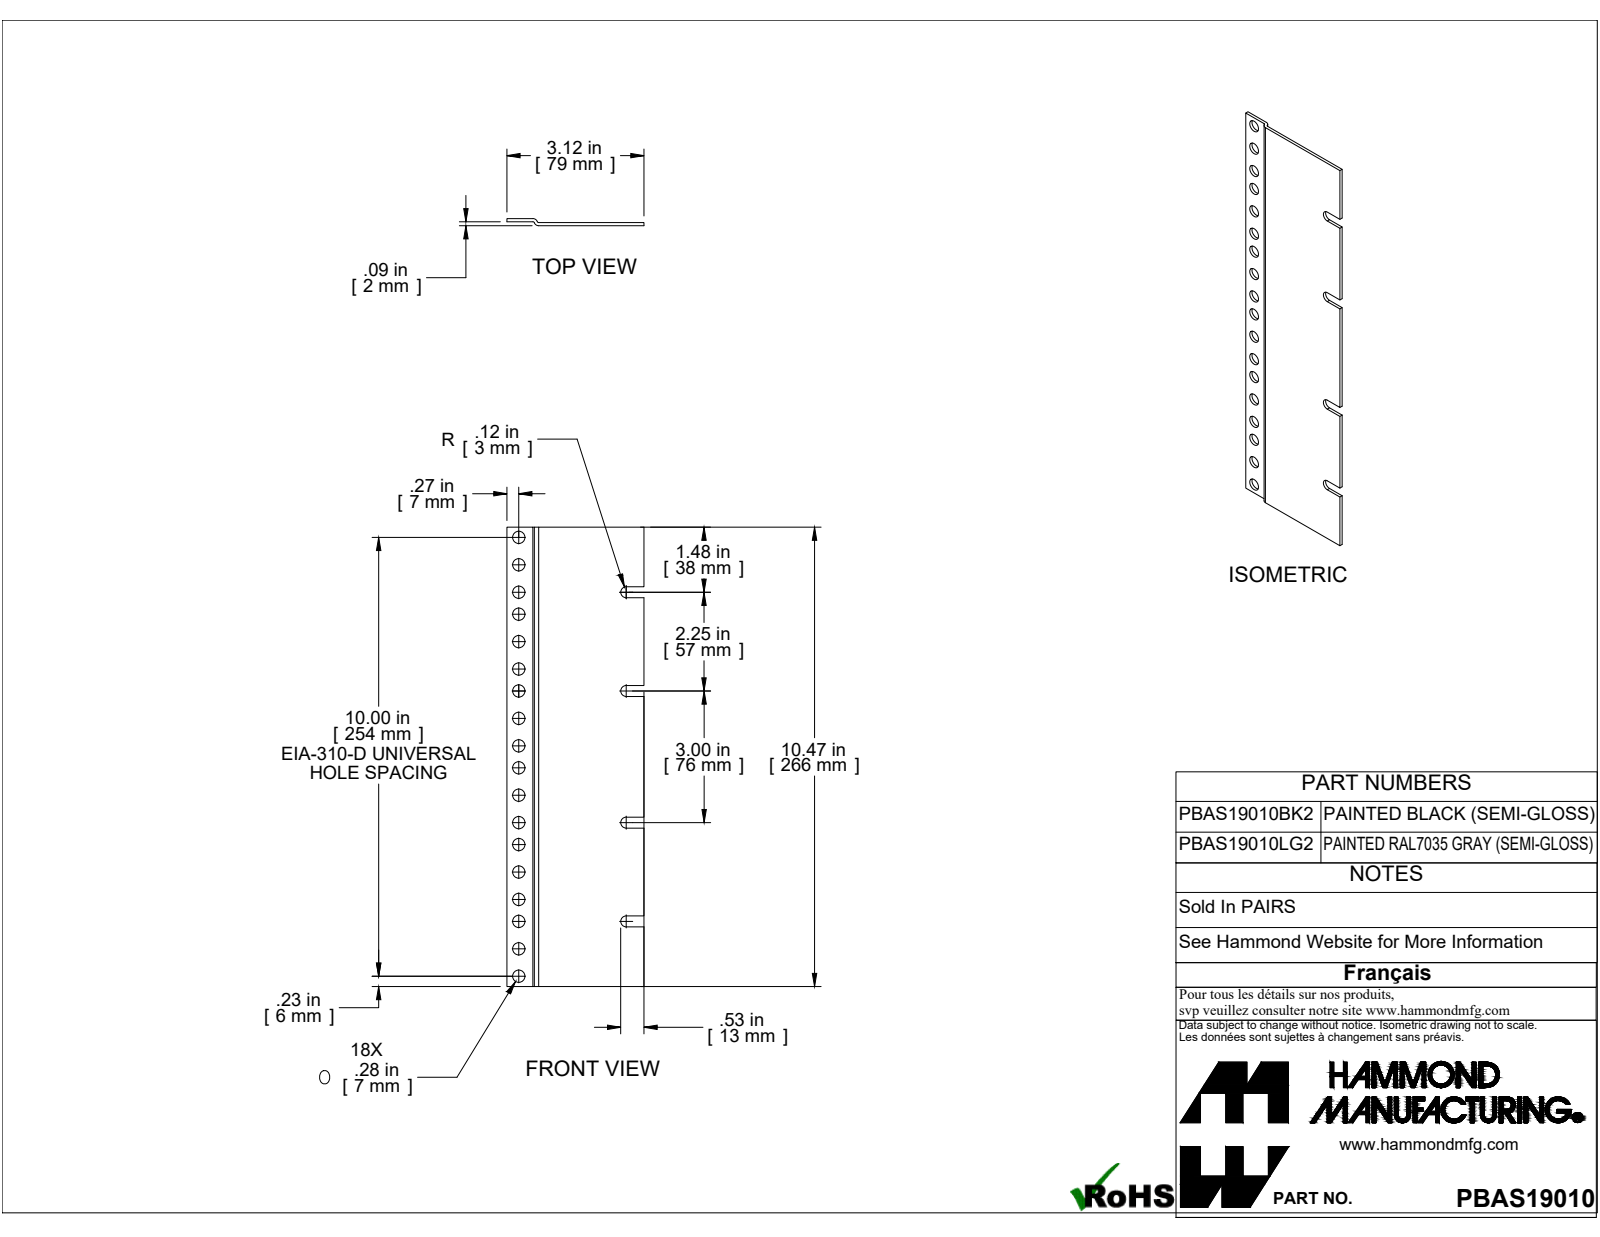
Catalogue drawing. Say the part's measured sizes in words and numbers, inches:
The part is named "PBAS19010LG2". Its 3-D file was written by "SolidWorks 2019 (CONFIG_CONTROL_DESIGN)". It is 1 solid with 46 faces: 20 planar, 26 cylindrical and 0 other. Overall it measures 10.468 by 3.125 by 0.162 inches. Its volume is 2.267 cubic inches and its surface area 66.35 square inches. Round holes: 18 of diameter 0.281. Partial cylindrical surfaces (rounded edges, fillets, slot ends): 4 of radius 0.125, 2 of radius 0.036, 2 of radius 0.108. The main face-to-face distances are 0.072, 0.162, 0.09, 0.09, 0.018, 0.072, 3.125, 10.468, 2.25, 0.25. The hole center spacings are 1.75, 3.5, 0.625, 0.625, 1.125, 1.25, 2.375, 2.875.
